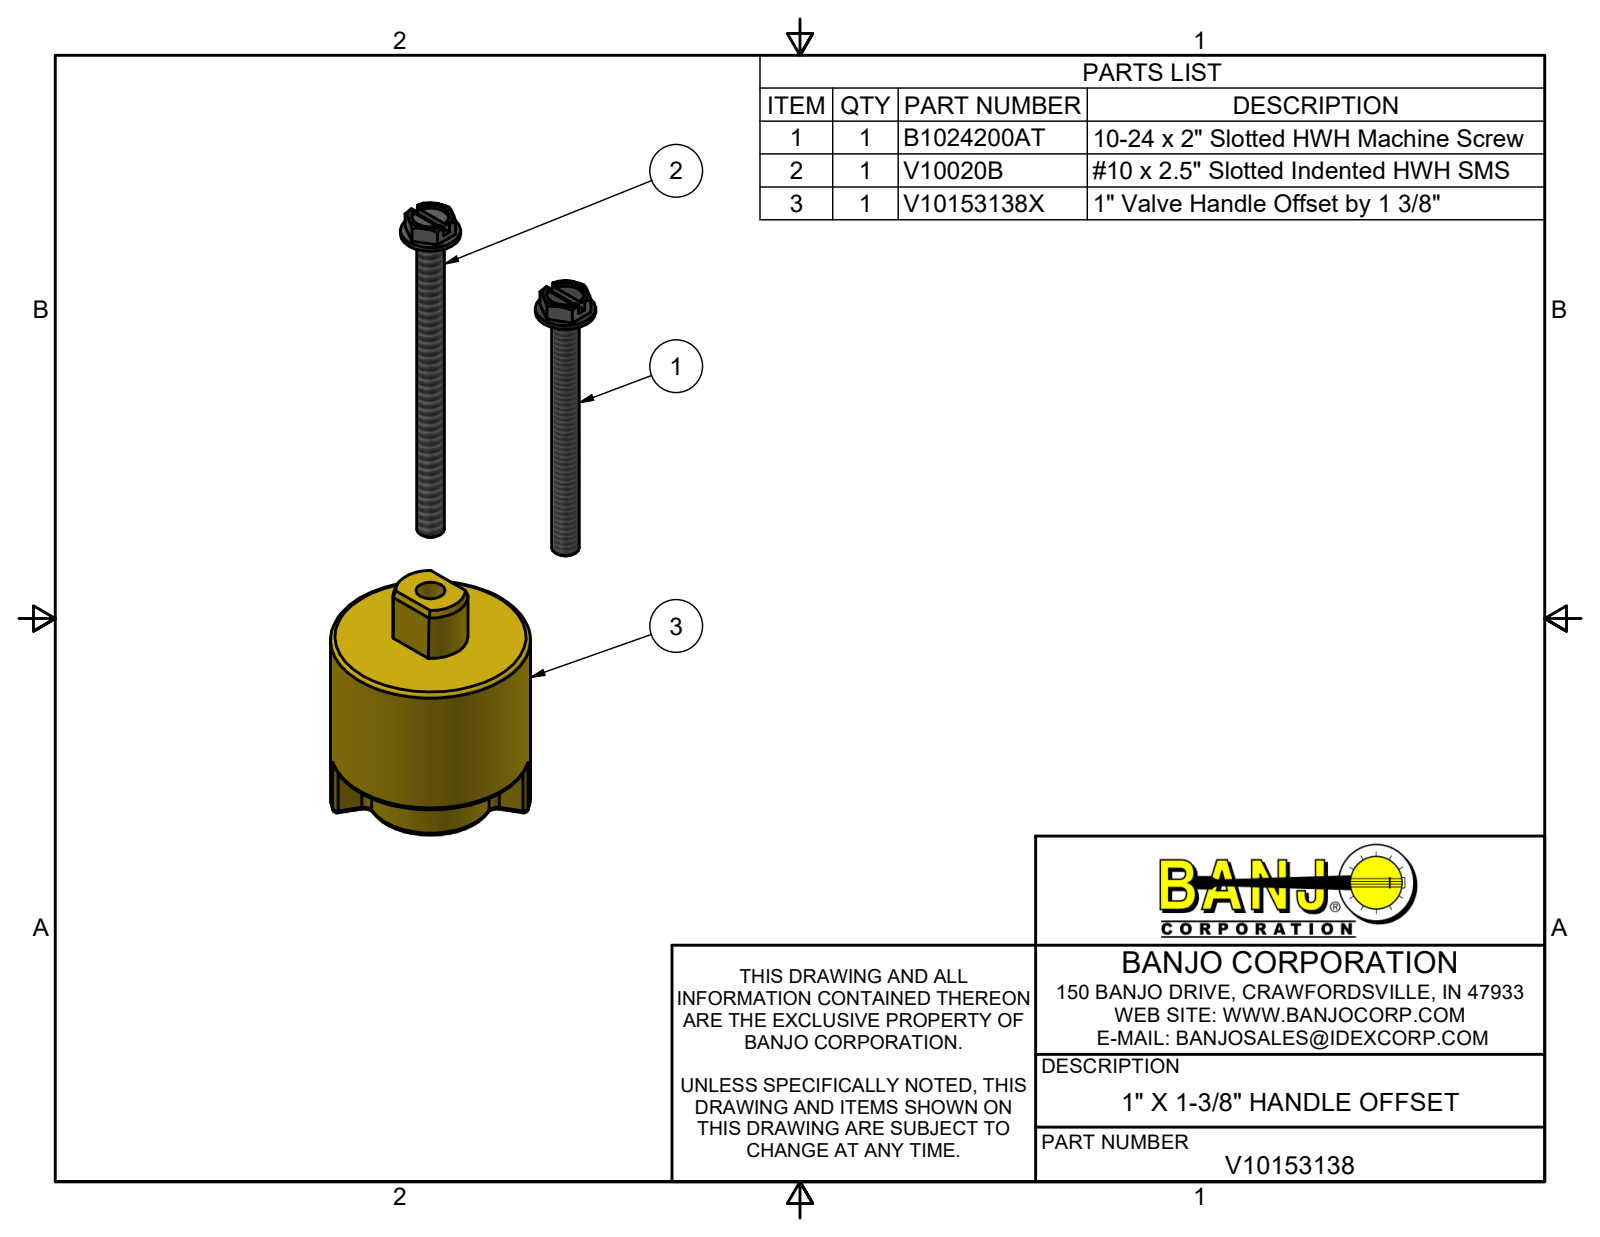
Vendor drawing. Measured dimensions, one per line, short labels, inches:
name: V10153138; V10153138X; V10020B; B1024200AT
written by: Autodesk Inventor 2022 (AUTOMOTIVE_DESIGN)
unit: in
bodies: 3 solids, 115 faces (50 planar, 34 cylindrical, 31 other)
size: 4.916 × 2.206 × 1.375
volume: 1.608 in³; area: 18.85 in²
holes: 2× ⌀0.26, 1× ⌀0.2
bosses: 2× ⌀0.414, 2× ⌀0.19, 1× ⌀1.375
rounds: 8× R0.03, 4× R0.058, 3× R0.057, 1× R0.058, 1× R0.257, 1× R0.435, 1× R0.55
face distances: 0.985, 0.39, 1.375, 1.25, 0.86, 0.125, 4.765, 4.375, 3.515, 3.39
hole spacings: 1.312
